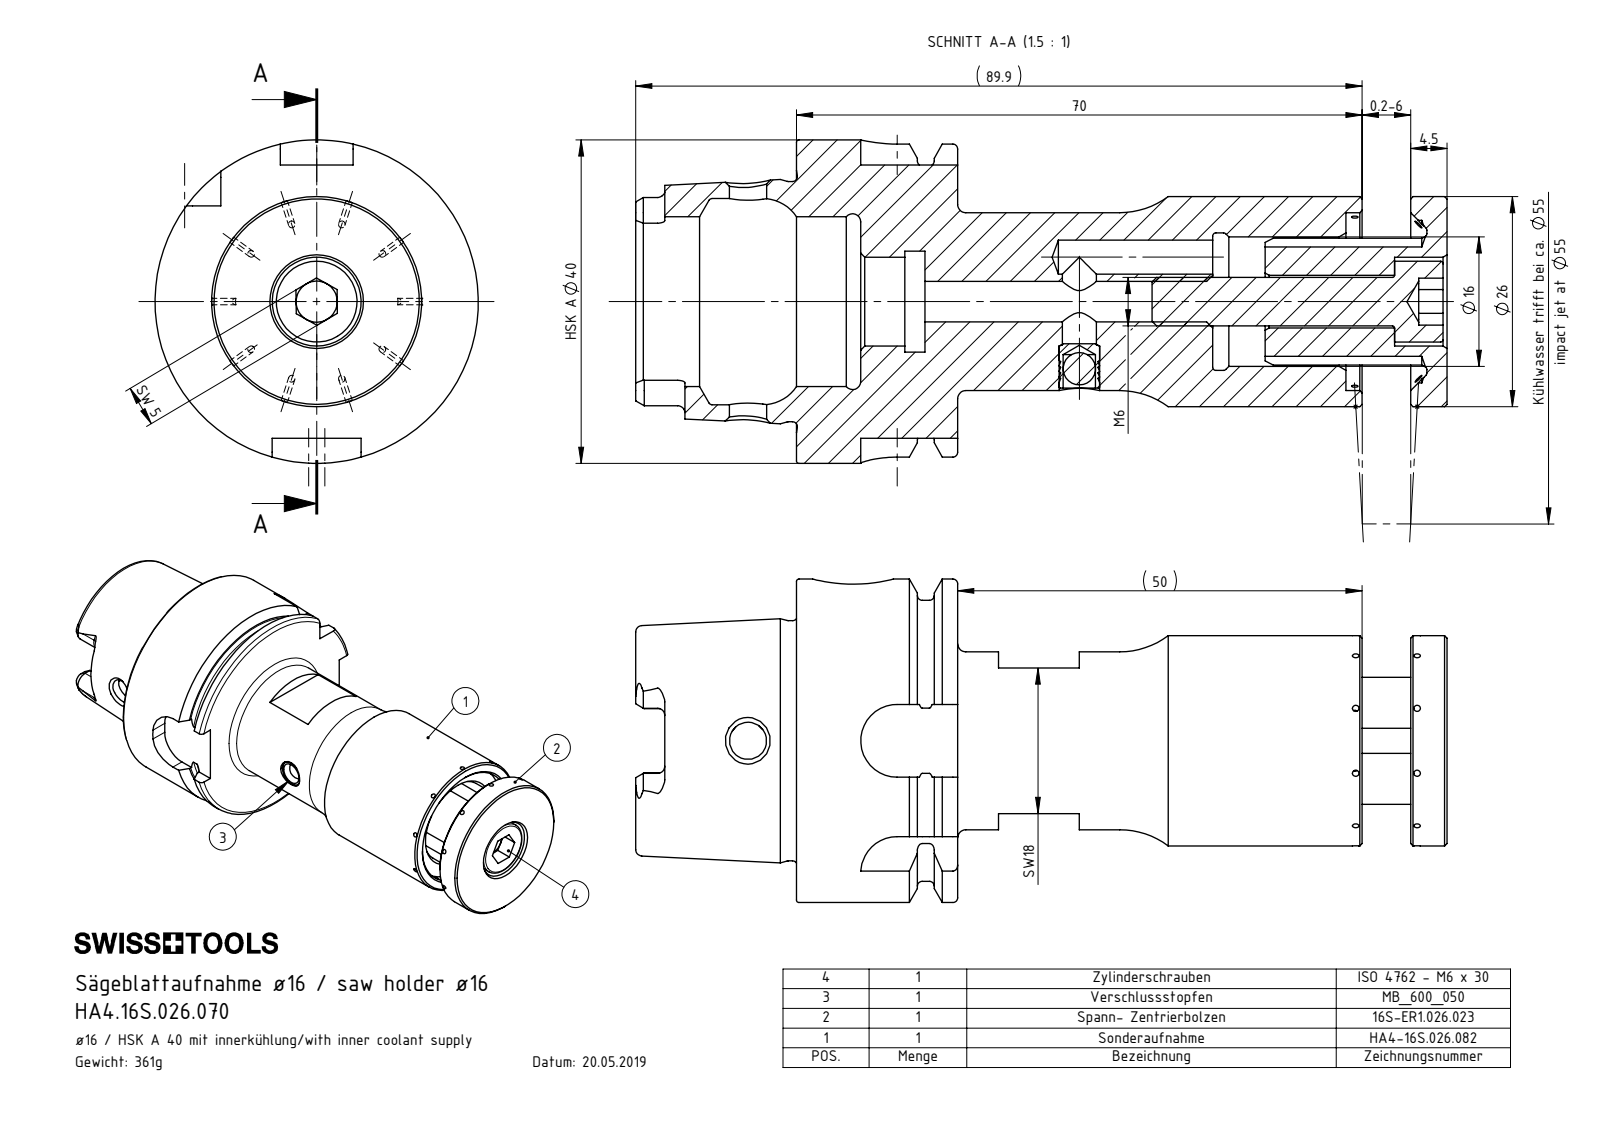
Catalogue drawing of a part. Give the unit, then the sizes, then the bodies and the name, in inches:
Units: inches
Overall size (bounding box): 3.953 × 1.575 × 1.575
Round holes (diameter × count): ⌀0.031 ×20, ⌀0.165 ×2, ⌀0.157 ×1, ⌀0.181 ×1, ⌀0.197 ×1, ⌀0.256 ×1, ⌀0.394 ×1, ⌀0.433 ×1, ⌀0.492 ×1, ⌀0.669 ×1, ⌀0.827 ×1, ⌀0.866 ×1
Round bosses / shafts (diameter × count): ⌀1.575 ×1, ⌀1.368 ×1, ⌀1.17 ×1, ⌀1.024 ×1, ⌀0.63 ×1, ⌀0.394 ×1, ⌀0.236 ×1, ⌀0.197 ×1
Partial cylindrical surfaces — rounded edges, fillets, slot ends (radius × count): R0.035 ×6, R0.065 ×4, R0.074 ×4, R0.177 ×4
Main face-to-face distances: 2.384, 0.785, 3.169, 0.472, 0.313, 0.236, 0.709, 0.256, 0.886, 1.97
Hole centre spacings: 0.356, 0.357, 0.217, 1.614
Volume: 2.876 in³ · Surface area: 30.39 in²
Bodies: 5 solids, 243 faces (74 planar, 82 cylindrical, 87 other)
Part name (STEP PRODUCT): ISO 4762 - M6 x 30; KVT_MB_600_050; 16S-ER1.026.023_A; HA4-16S.026.070_A_Fertigbearbeitung (+1 more)
STEP written by: SolidWorks 2017 (AUTOMOTIVE_DESIGN)
